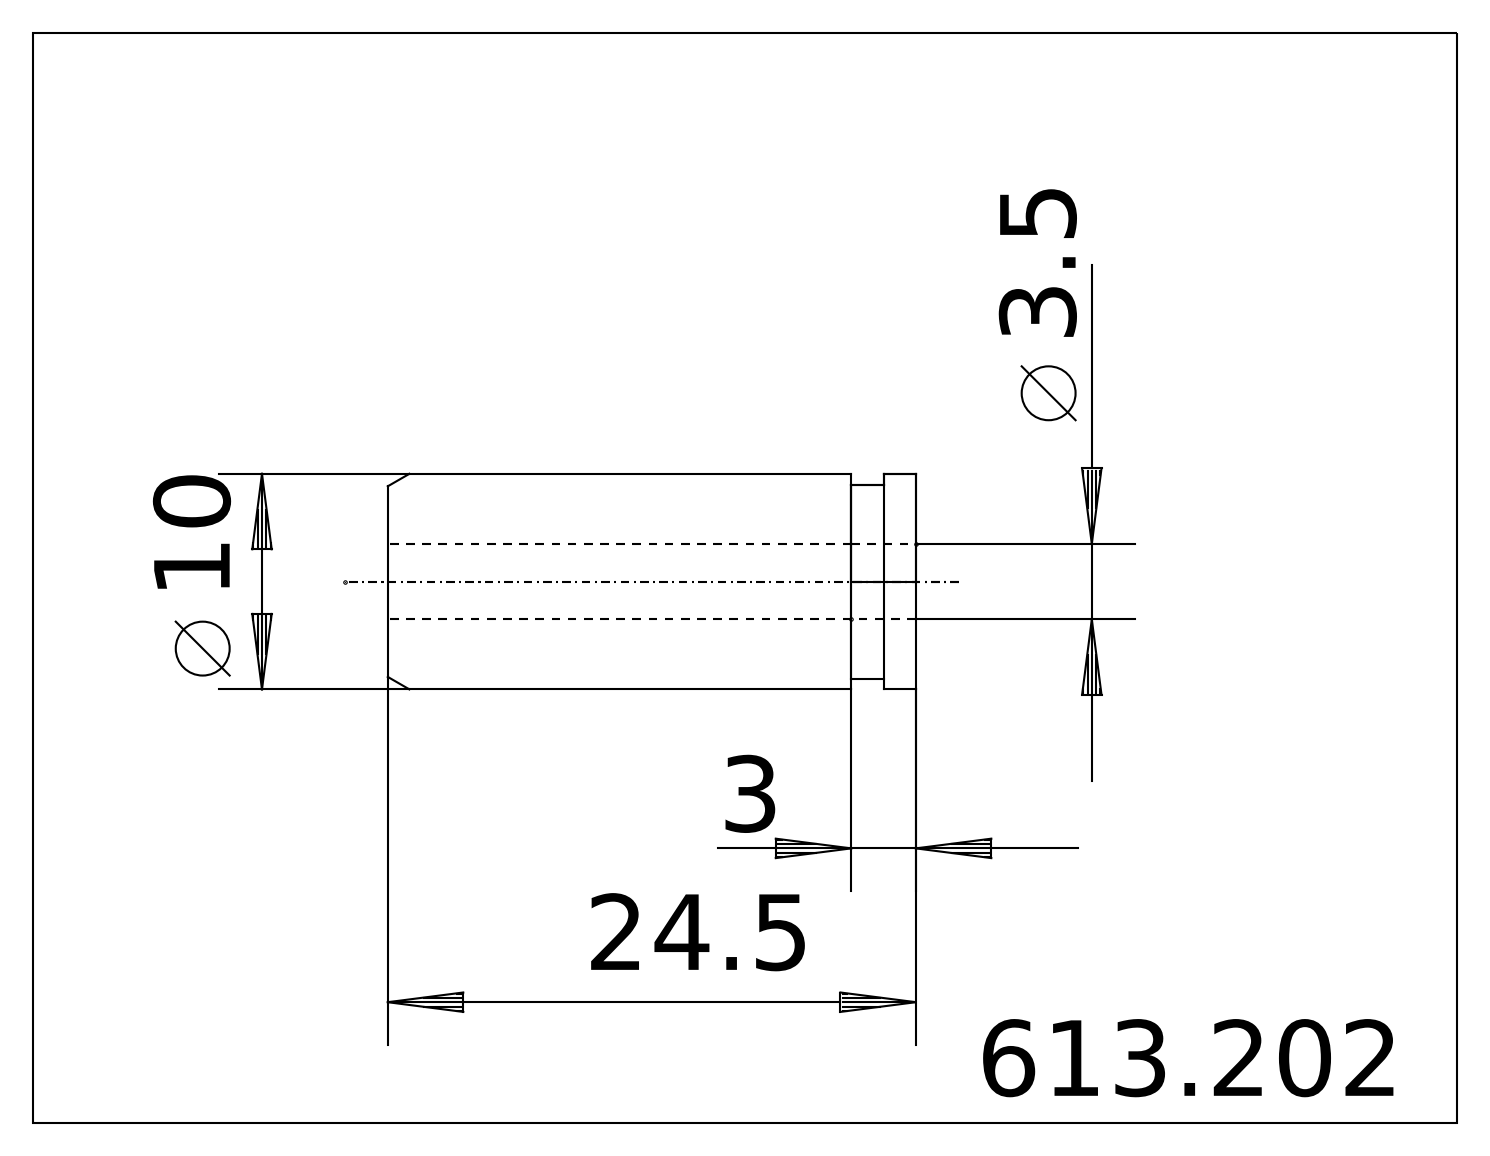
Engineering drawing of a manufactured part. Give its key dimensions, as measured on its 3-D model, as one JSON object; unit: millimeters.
{"step_written_by": "ACIS (automotive_design)", "units": "millimeters", "bodies": {"solids": 1, "faces": 18, "planar": 4, "cylindrical": 8, "other": 6}, "overall_size": [24.5, 10, 10], "volume_mm3": 1653, "surface_area_mm2": 1176, "round_holes": [[3.5, 1]], "round_bosses_or_shafts": [[10, 1], [9, 1]], "face_to_face_distances": [24.5, 1.5, 3, 21.5, 23]}
